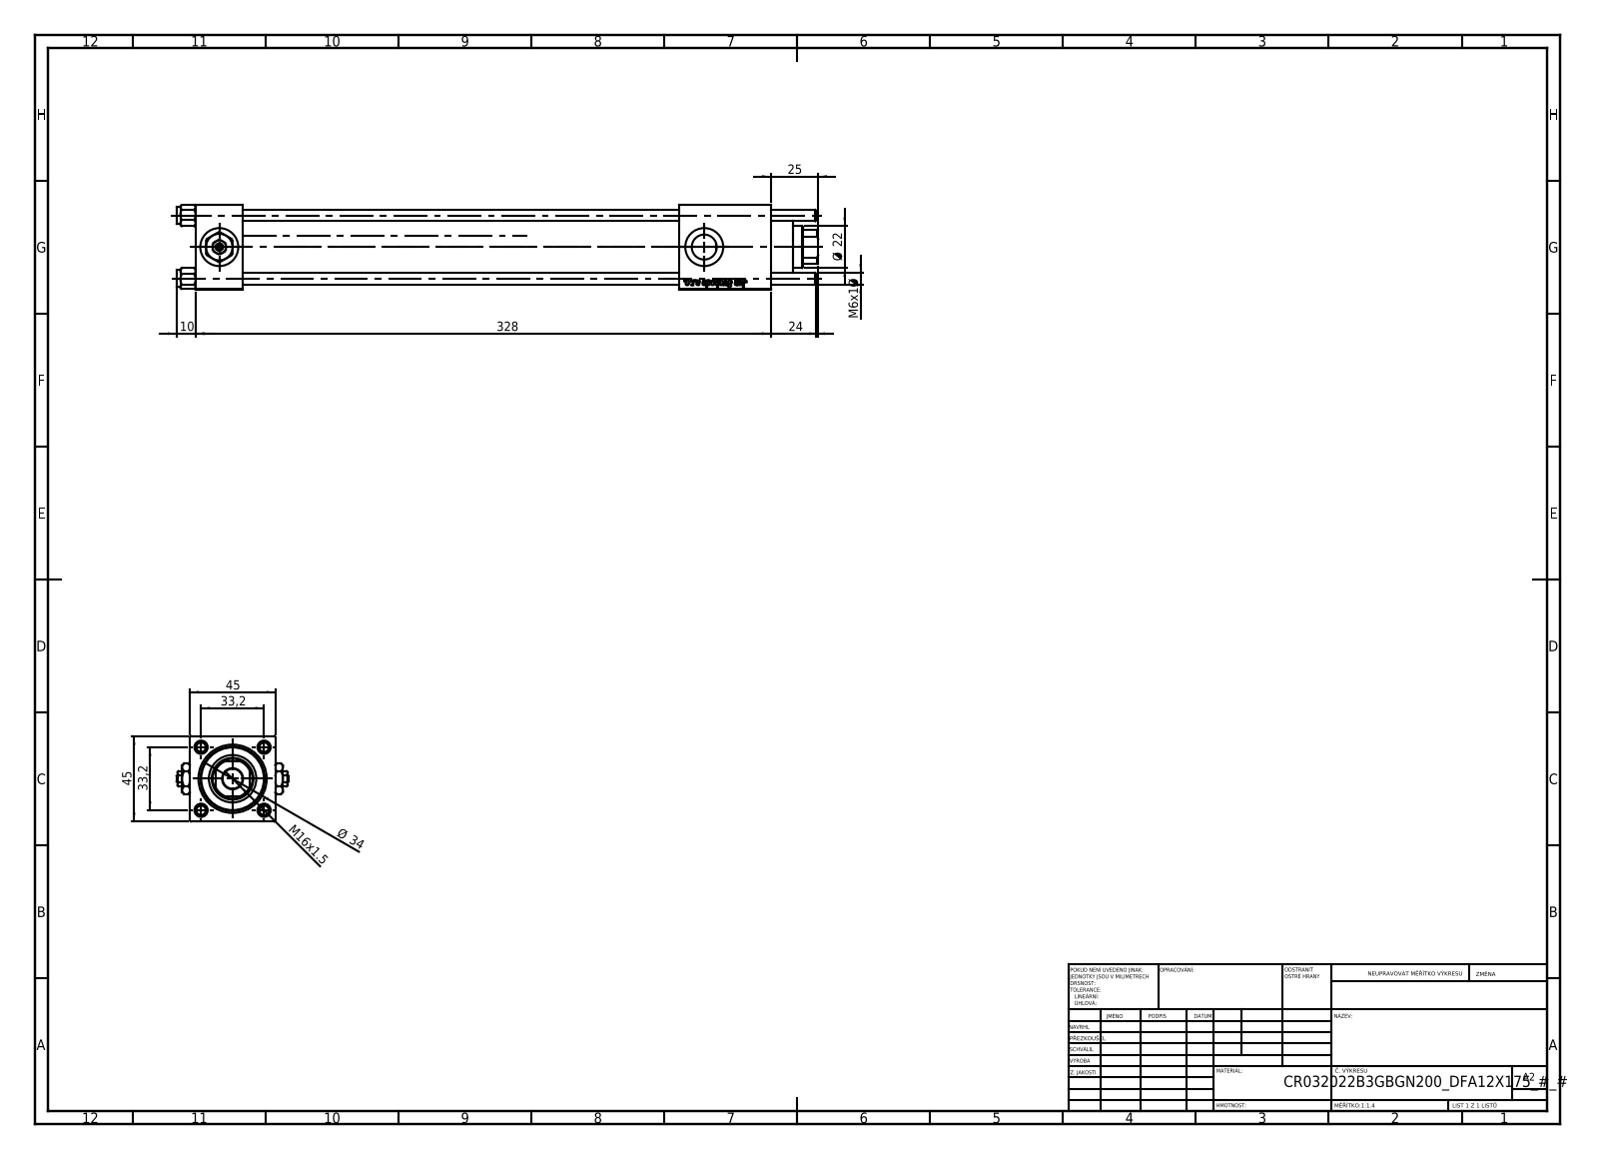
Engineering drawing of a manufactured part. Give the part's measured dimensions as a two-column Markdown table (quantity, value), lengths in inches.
| quantity | value |
| --- | --- |
| part name | FEMALE_PART_FOR_DFA; Zatka_pro_OIL_PORT; V215CR_VCP_B; V215CR_B-1 (+3 more) |
| STEP written by | SolidWorks 2019 (CONFIG_CONTROL_DESIGN) |
| units | inches |
| bodies | 14 solids, 1289 faces (490 planar, 97 cylindrical, 702 other) |
| overall size | 13.307 × 2.323 × 1.772 |
| volume | 22.62 in³ |
| surface area | 230.4 in² |
| round holes (diameter × count) | 0.236 × 4, 0.276 × 2, 0.518 × 2, 0.787 × 2, 0.413 × 1, 0.866 × 1, 0.945 × 1, 0.984 × 1, 1.26 × 1, 1.299 × 1 |
| round bosses / shafts (diameter × count) | 0.354 × 4, 1.496 × 1, 1.339 × 1, 1.102 × 1, 0.472 × 1, 0.394 × 1 |
| partial cylindrical surfaces (radius × count) | 0.384 × 1, 0.413 × 1 |
| main face-to-face distances | 1.772, 0.984, 11.929, 10.039, 9.055, 1.764, 10.945, 1.89, 10.799, 9.815 |
| hole center spacings | 0.924, 1.307, 1.848, 10.059 |
